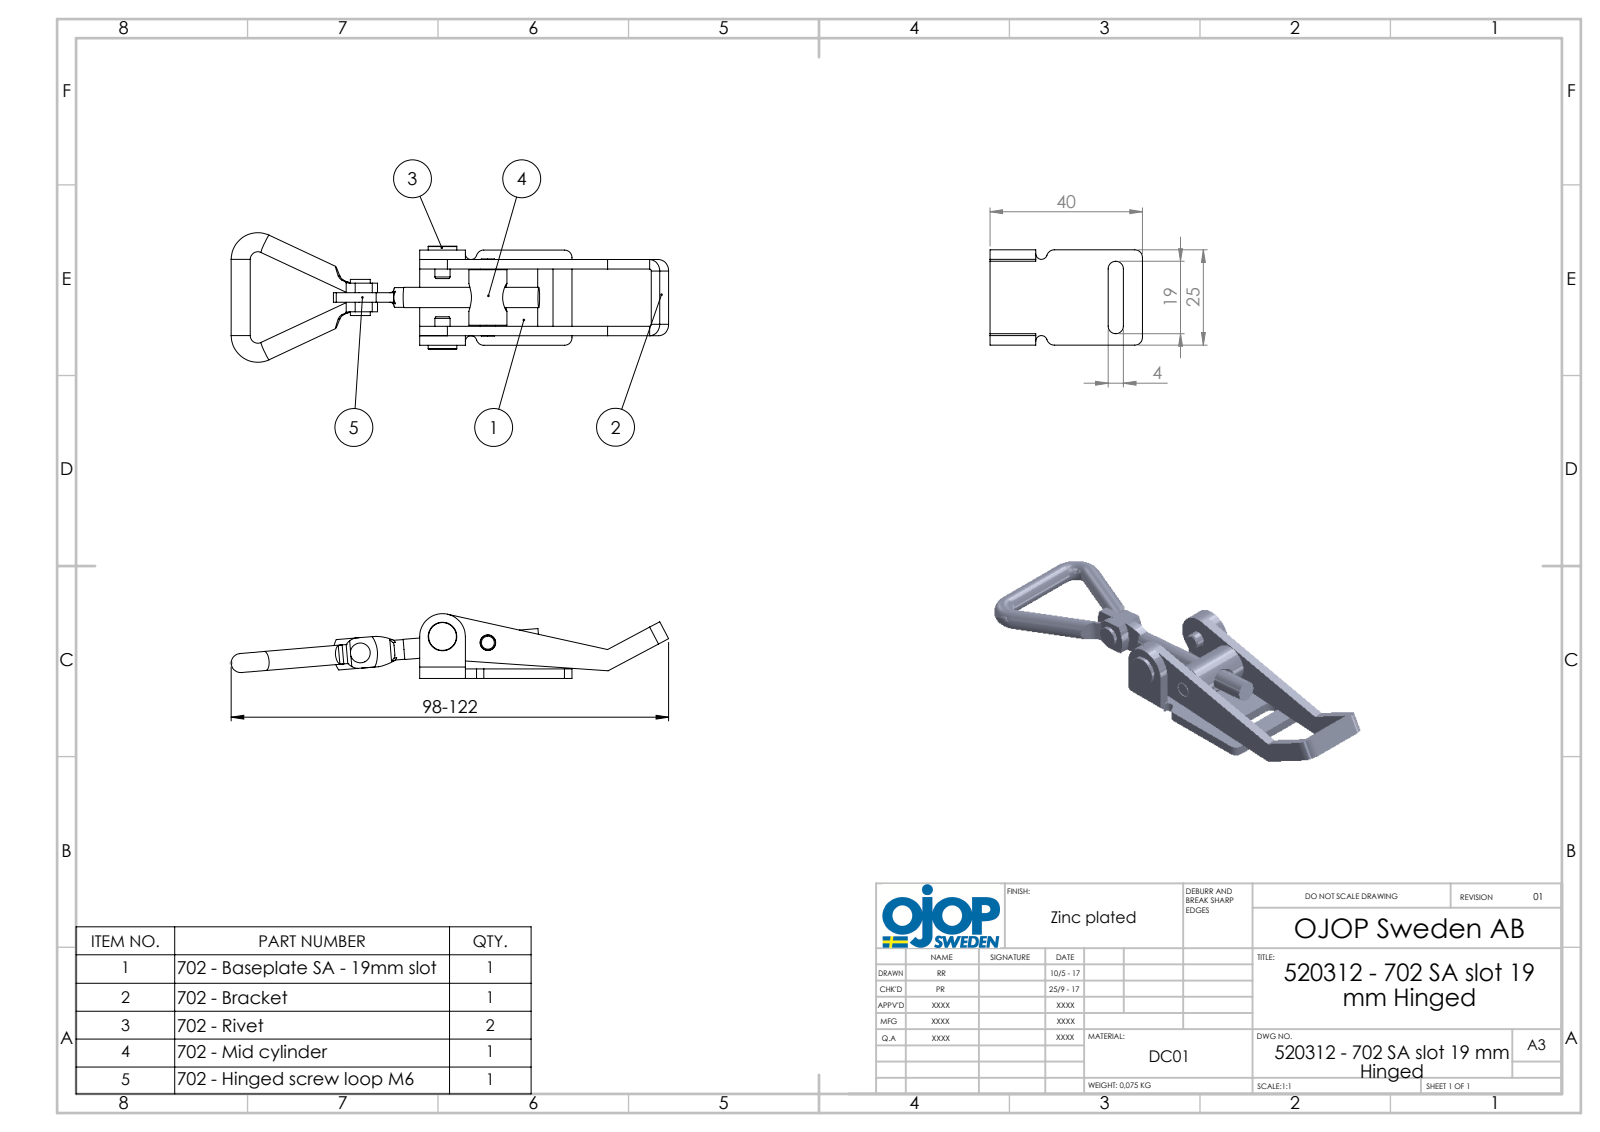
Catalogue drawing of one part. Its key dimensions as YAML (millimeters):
part_name: "520312 - 702 SA slits 19 mm; 702 - Ring till ledad M6; 702 - Skruv till ledad M6; 702 - Ring 702 M6 (+5 more)"
step_written_by: "SolidWorks 2015 (AUTOMOTIVE_DESIGN)"
units: millimeters
bodies: {solids: 8, faces: 204, planar: 82, cylindrical: 100, other: 22}
overall_size: [114.83, 34, 17]
volume: 10033
surface_area: 10124
round_holes:
  - {diameter: 4.1, count: 3}
  - {diameter: 5, count: 1}
  - {diameter: 6, count: 1}
round_bosses_or_shafts:
  - {diameter: 5, count: 3}
  - {diameter: 4, count: 2}
  - {diameter: 10, count: 1}
  - {diameter: 7.5, count: 1}
  - {diameter: 5.3, count: 1}
  - {diameter: 5.2, count: 1}
  - {diameter: 5.18, count: 1}
partial_cylinders:
  - {radius: 2, count: 10}
  - {radius: 1, count: 6}
  - {radius: 0.5, count: 4}
  - {radius: 3, count: 4}
  - {radius: 1.5, count: 2}
  - {radius: 6.78, count: 2}
  - {radius: 12.31, count: 2}
  - {radius: 3.85, count: 1}
face_to_face_distances: [2.5, 20, 17.5, 5, 15, 22.5, 8.8, 8.7, 11.2, 11.3]
hole_center_spacings: [12.02, 22, 33.6]
